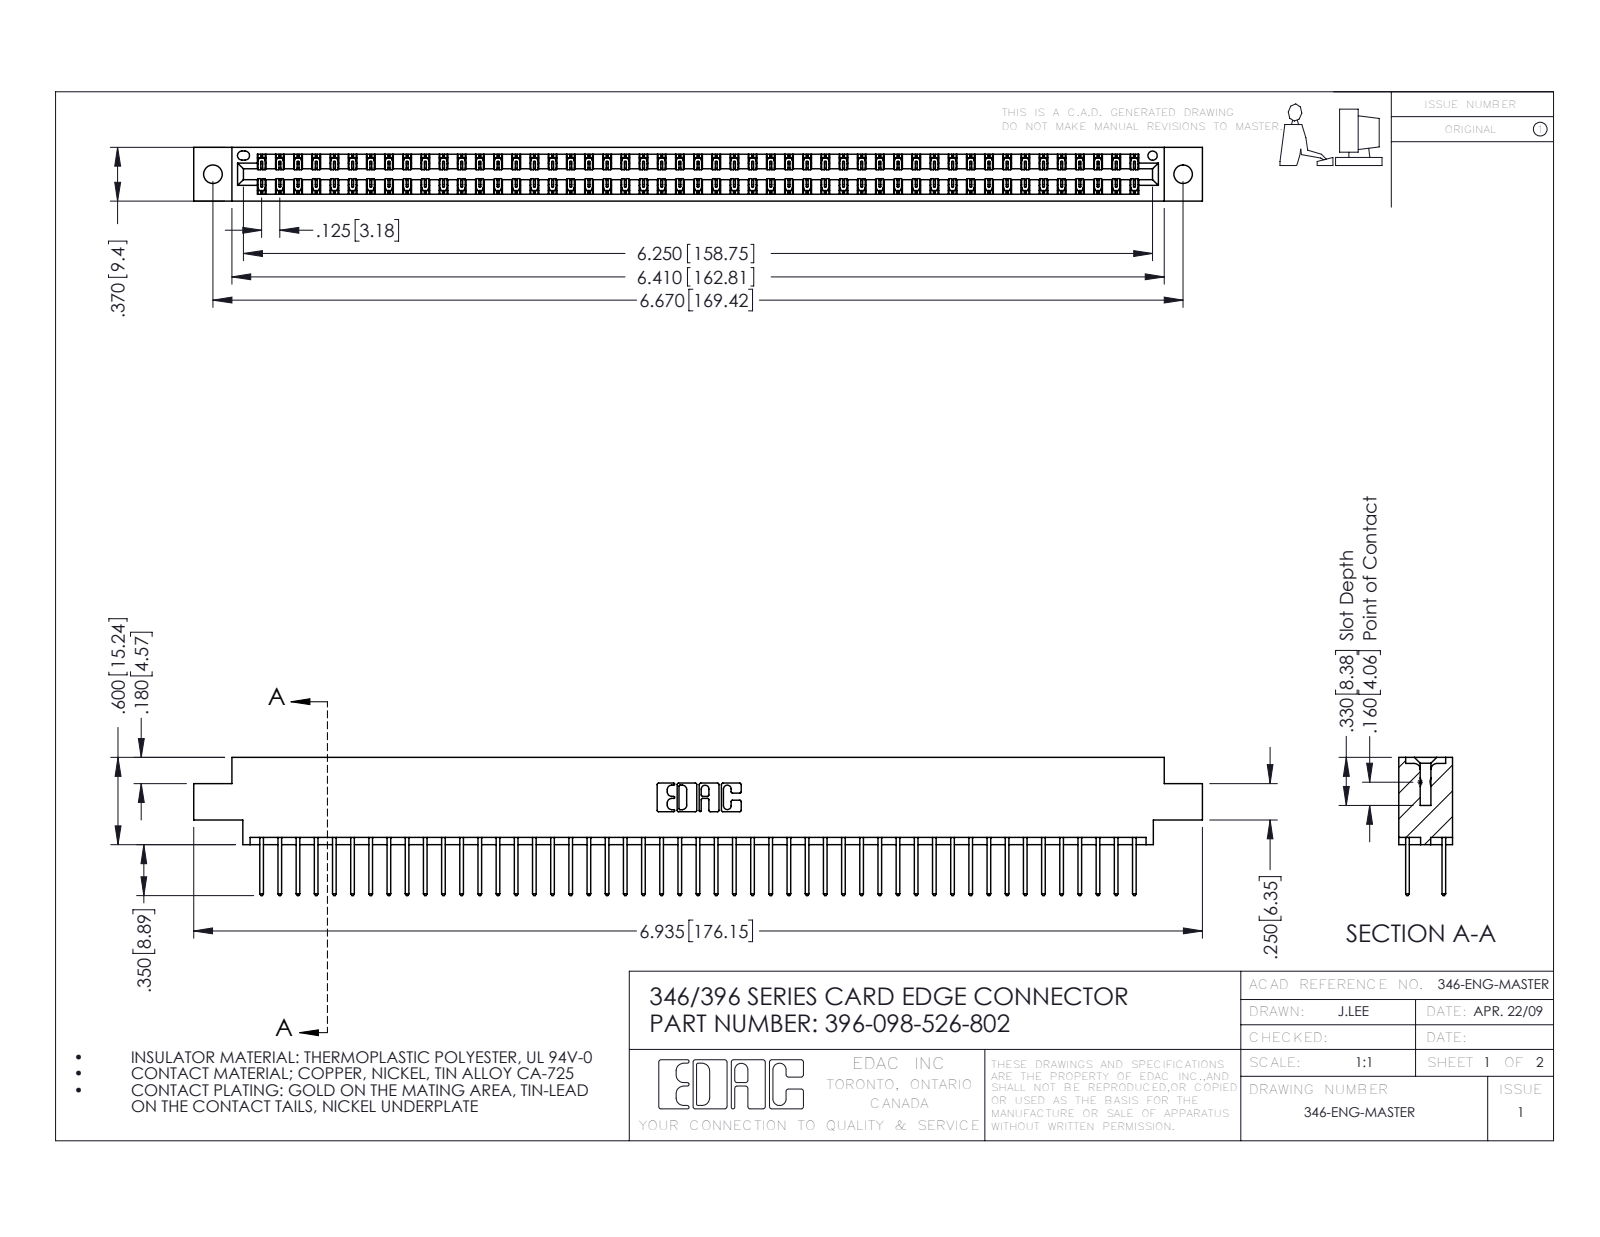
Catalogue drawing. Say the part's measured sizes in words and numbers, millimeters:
The part is named "346 Part_0.170 Offset - 0.128 Dia; 396-098-526-802; 345-292-001_345-293-126". Its 3-D file was written by "SolidWorks 2016 (CONFIG_CONTROL_DESIGN)". It is 99 solids with 5222 faces: 3510 planar, 1712 cylindrical and 0 other. Overall it measures 176.1 by 24.1 by 9.4 millimeters. Its volume is 17 210 cubic millimeters and its surface area 24 380 square millimeters. Round holes: 2 of diameter 3.3, 1 of diameter 1.6. Partial cylindrical surfaces (rounded edges, fillets, slot ends): 147 of radius 0.2, 98 of radius 0.3, 22 of radius 0.3, 6 of radius 0.2, 6 of radius 0.8, 3 of radius 0.7, 2 of radius 0.4, 2 of radius 0.6. The main face-to-face distances are 1.2, 8.2, 6.4, 9.4, 1.8, 7.6, 0.6, 7, 3.8, 5.6. The hole center spacings are 6.2, 164.1, 169.4.
